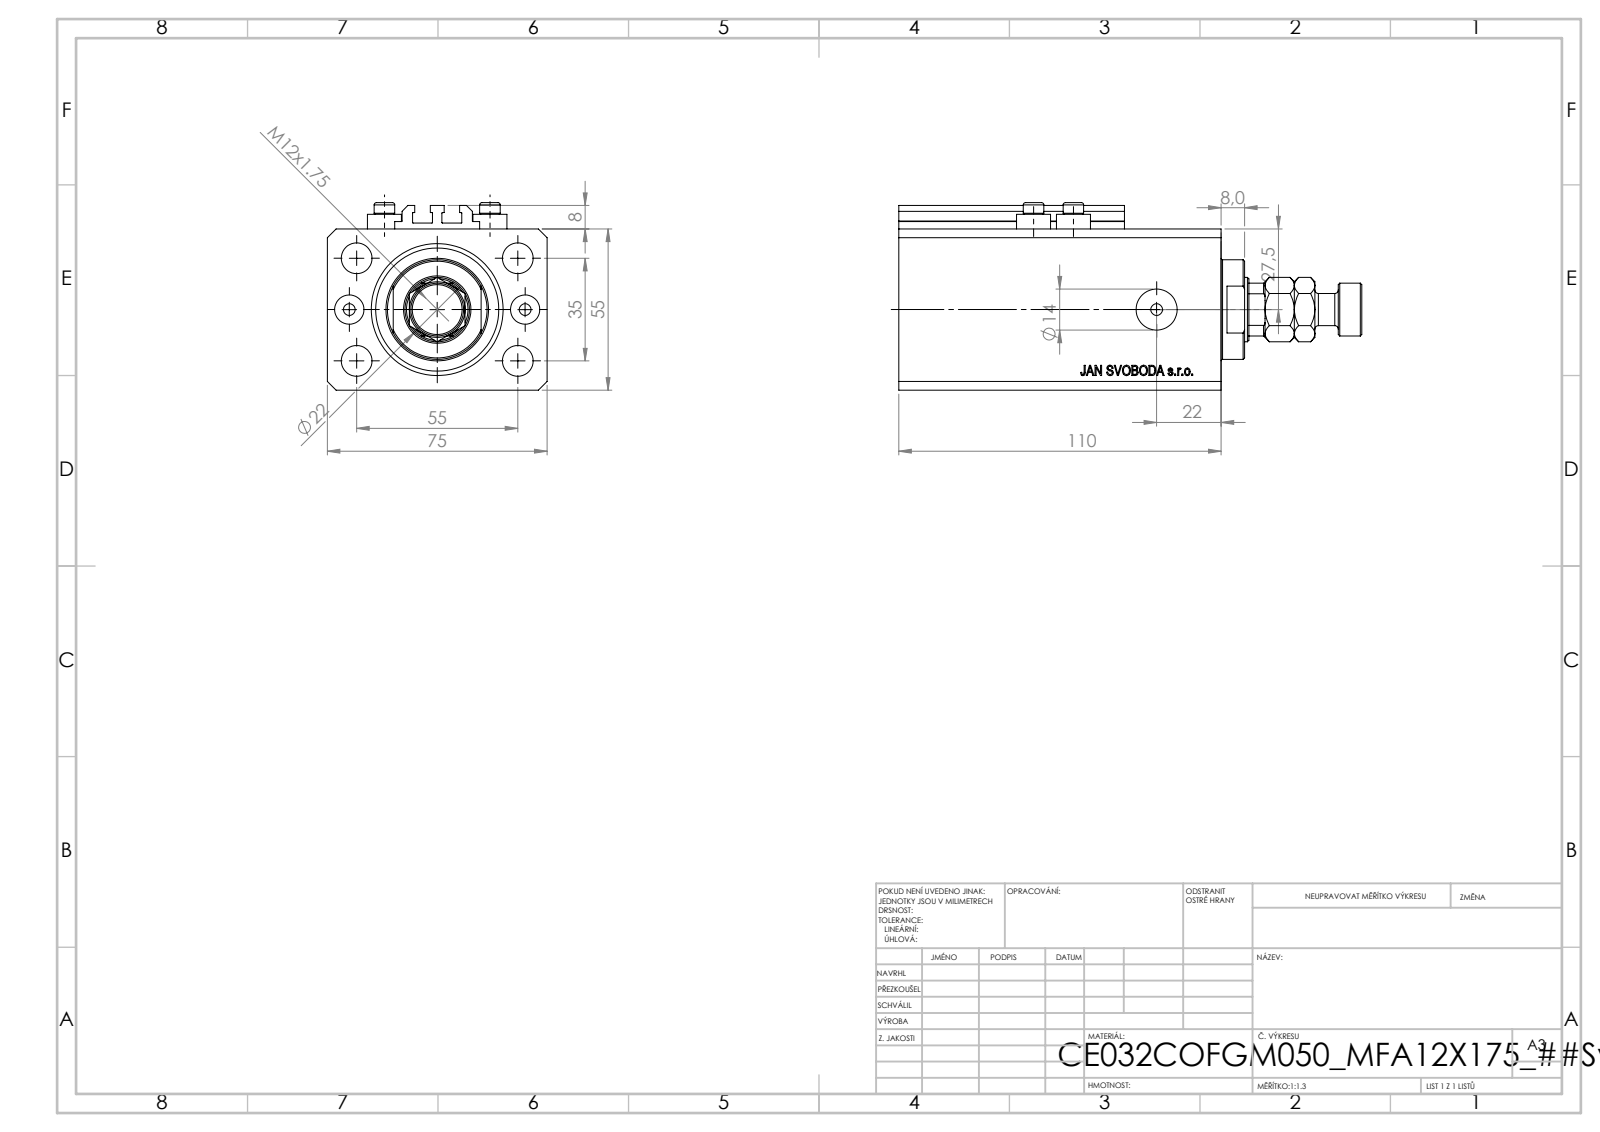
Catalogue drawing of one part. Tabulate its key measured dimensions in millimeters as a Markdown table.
| quantity | value |
| --- | --- |
| part name | V250CE_VC_C; V250CE_C_Body; V250CE_C_VCP; ALLEN BOLT V250CE (+1 more) |
| STEP written by | SolidWorks 2019 (CONFIG_CONTROL_DESIGN) |
| units | millimeters |
| bodies | 9 solids, 1086 faces (520 planar, 90 cylindrical, 476 other) |
| overall size | 158 × 75 × 64 |
| volume | 416 999 mm³ |
| surface area | 93 814 mm² |
| round holes (diameter × count) | 4 × 8, 10.5 × 5, 10 × 2, 14 × 2, 22 × 1, 32 × 1, 45 × 1 |
| round bosses / shafts (diameter × count) | 11.6 × 4, 7 × 4, 34 × 1, 18 × 1, 11 × 1 |
| partial cylindrical surfaces (radius × count) | 0.2 × 10, 10.5 × 1 |
| main face-to-face distances | 55, 75, 15, 110, 95, 9.9, 85.1, 100.1, 2.5, 8 |
| hole center spacings | 17.68, 32.6, 60.1, 13.6, 30, 35, 36, 38.48 |
